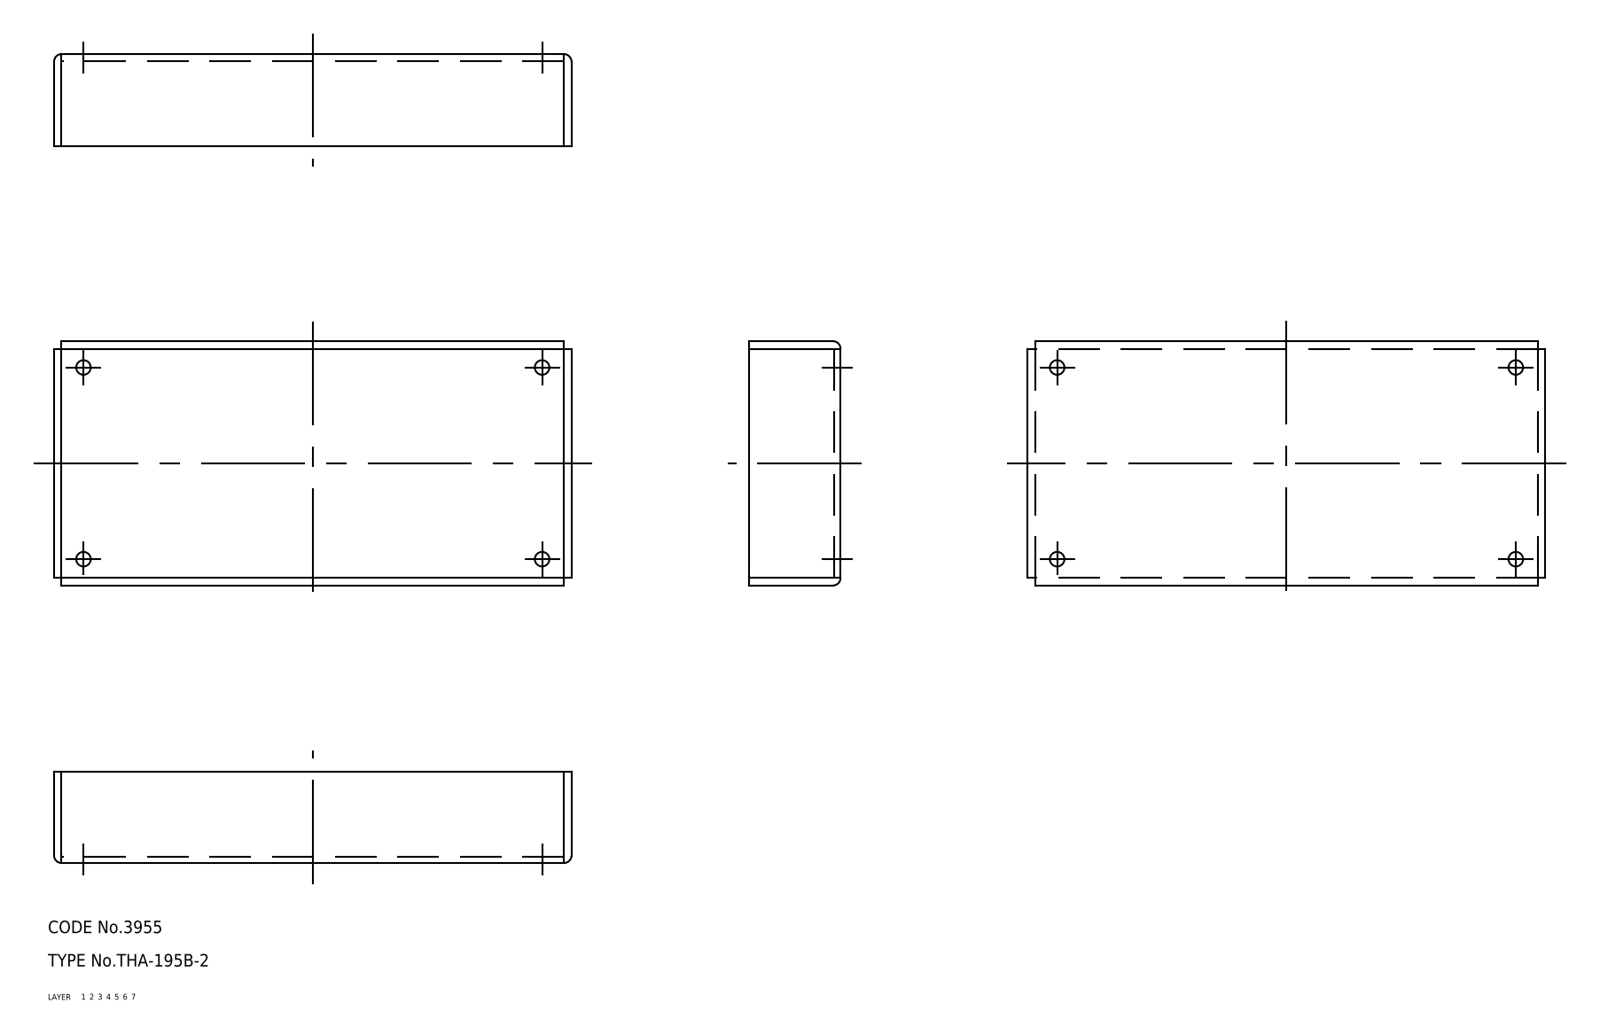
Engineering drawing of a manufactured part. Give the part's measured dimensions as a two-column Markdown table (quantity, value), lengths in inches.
| quantity | value |
| --- | --- |
| part name | bracket |
| STEP written by | CADfix (AUTOMOTIVE_DESIGN) |
| units | inches |
| bodies | 1 solid, 34 faces (0 planar, 0 cylindrical, 34 other) |
| overall size | 4.886 × 2.307 × 0.866 |
| volume | 1.474 in³ |
| surface area | 45.62 in² |
